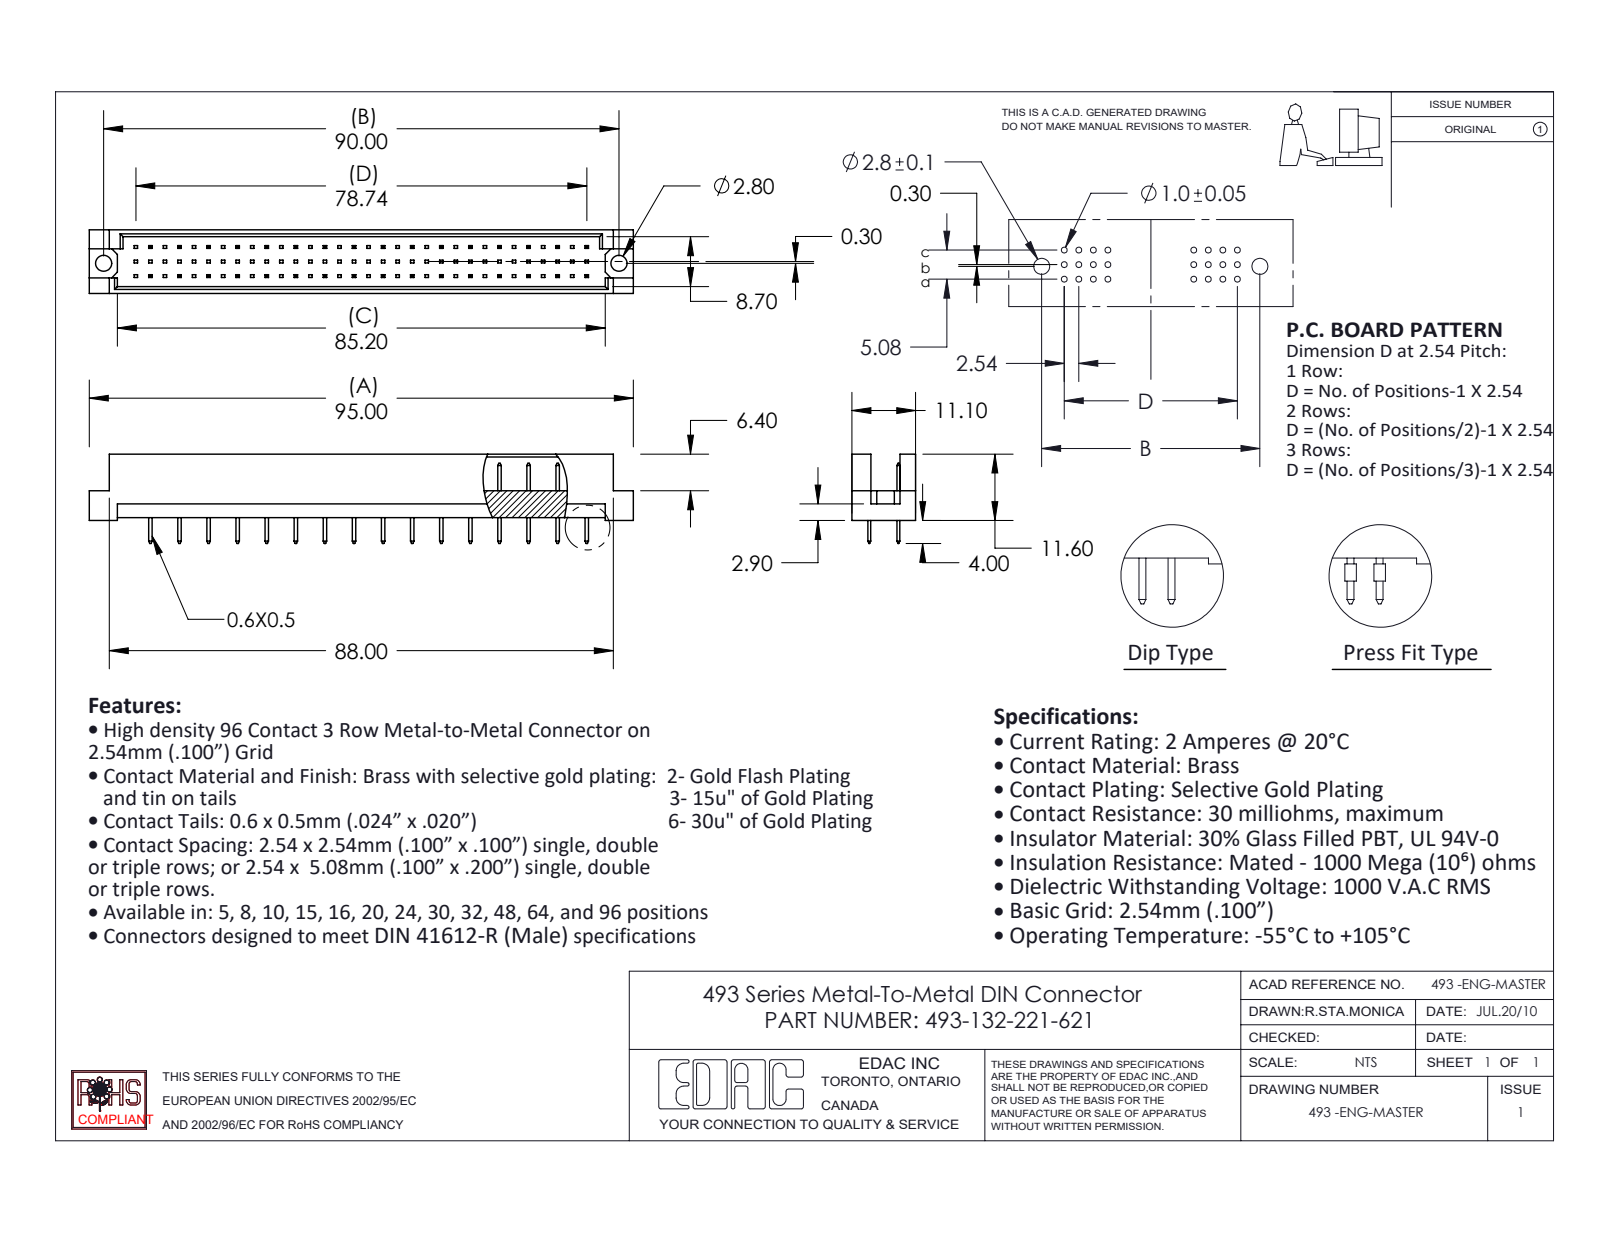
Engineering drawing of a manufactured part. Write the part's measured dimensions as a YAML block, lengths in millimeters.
part_name: "493-290_21; 493-132-221-621; 493 Part_96"
step_written_by: "SolidWorks 2020 (CONFIG_CONTROL_DESIGN)"
units: millimeters
bodies: {solids: 33, faces: 884, planar: 880, cylindrical: 4, other: 0}
overall_size: [95, 15.6, 11.1]
volume: 5790
surface_area: 7448
round_holes:
  - {diameter: 2.8, count: 2}
face_to_face_distances: [1.2, 9.9, 11.1, 8.7, 5.08, 4.7, 0.5, 2.76, 3.26, 7.84]
hole_center_spacings: [90]
